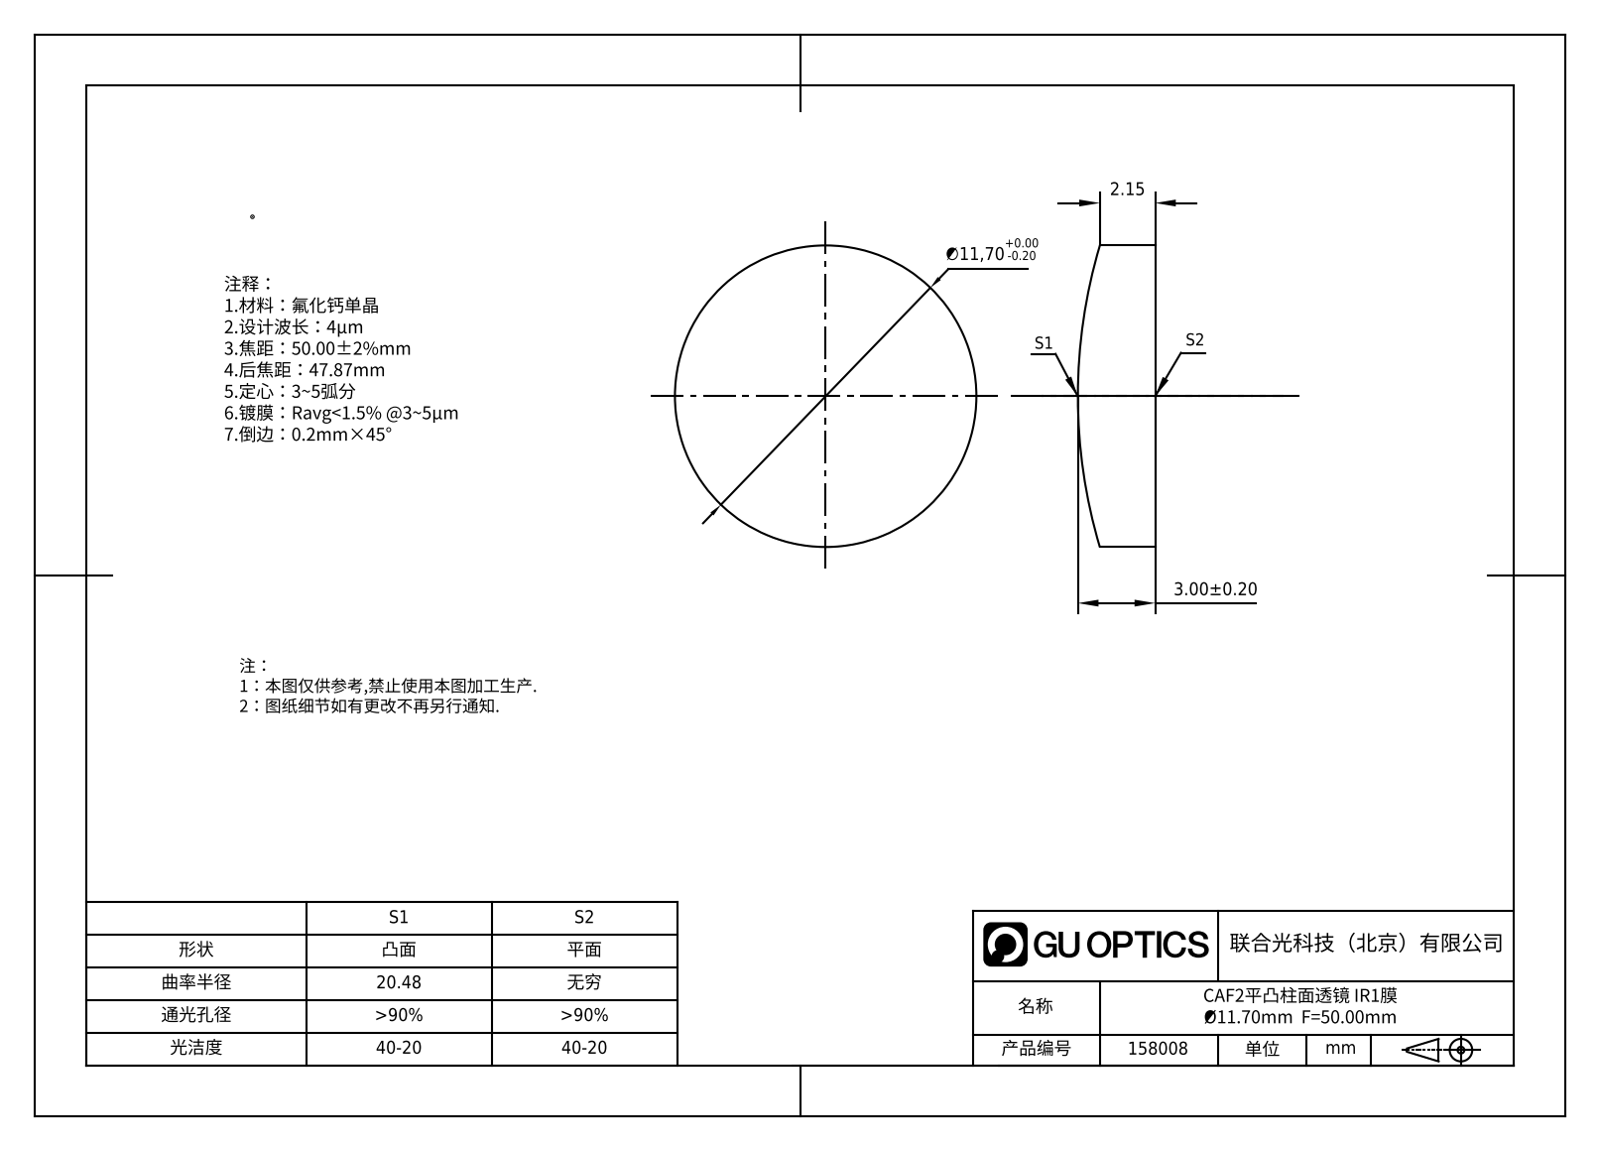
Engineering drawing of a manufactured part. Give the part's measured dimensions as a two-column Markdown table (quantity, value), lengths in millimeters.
| quantity | value |
| --- | --- |
| part name | GL55-012-050-IR1 |
| STEP written by | SolidWorks 2022 (AUTOMOTIVE_DESIGN) |
| units | millimeters |
| bodies | 1 solid, 9 faces (1 planar, 4 cylindrical, 4 other) |
| overall size | 11.7 × 11.7 × 3 |
| volume | 299 mm³ |
| surface area | 303 mm² |
| round bosses / shafts (diameter × count) | 11.7 × 1 |
| partial cylindrical surfaces (radius × count) | 20.48 × 1 |
